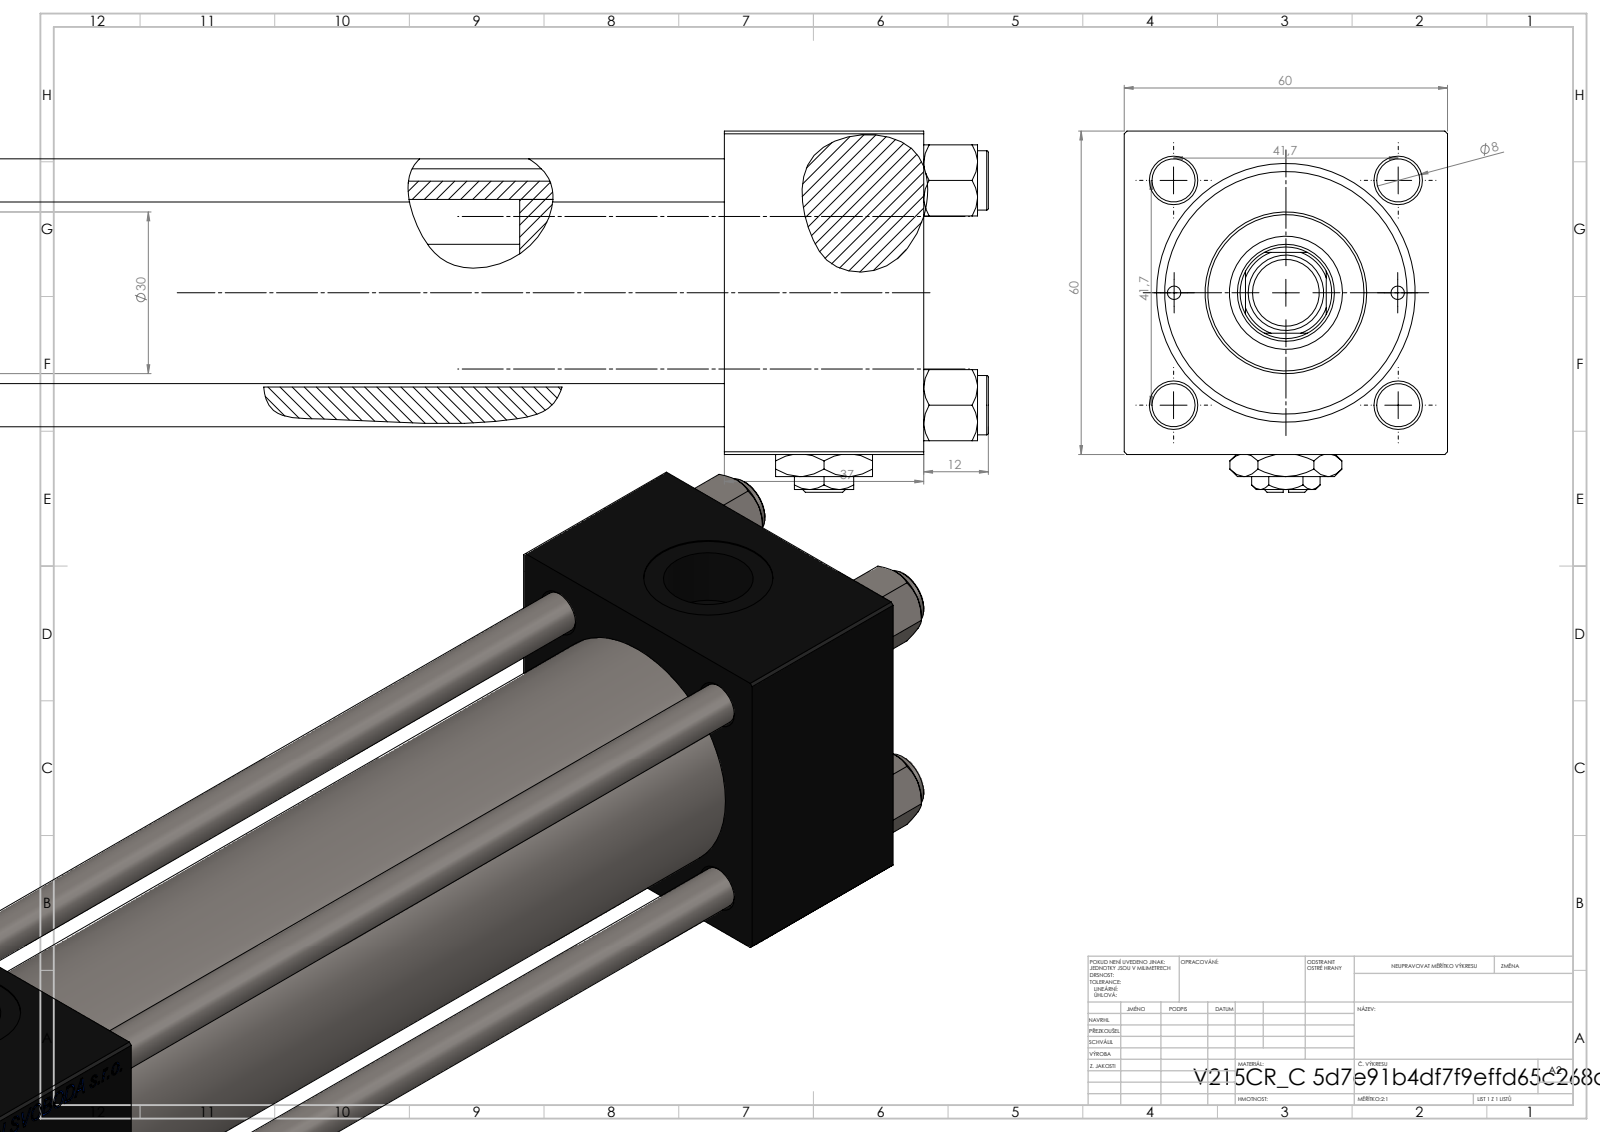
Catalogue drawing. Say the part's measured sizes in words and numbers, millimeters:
The part is named "V215_VC_A; NUT_M5_C; ROD_END_AH; Zatka_pro_OIL_PORT (+3 more)". Its 3-D file was written by "SolidWorks 2019 (CONFIG_CONTROL_DESIGN)". It is 14 solids with 1270 faces: 580 planar, 106 cylindrical and 584 other. Overall it measures 308 by 67 by 60 millimeters. Its volume is 491 848 cubic millimeters and its surface area 154 402 square millimeters. Round holes: 4 of diameter 8, 2 of diameter 2.5, 2 of diameter 7, 2 of diameter 16.66, 2 of diameter 24, 1 of diameter 8.5, 1 of diameter 18, 1 of diameter 21, 1 of diameter 31, 1 of diameter 40, 1 of diameter 45. Round bosses or shafts: 4 of diameter 11, 1 of diameter 46, 1 of diameter 30, 1 of diameter 14, 1 of diameter 12. Partial cylindrical surfaces (rounded edges, fillets, slot ends): 1 of radius 8.5. The main face-to-face distances are 60, 37, 253, 216, 53, 200, 163, 224.3, 187.3, 24.3. The hole center spacings are 20.85, 29.49, 41.7, 46.53, 20.75, 58.97, 41.5, 197.5.
